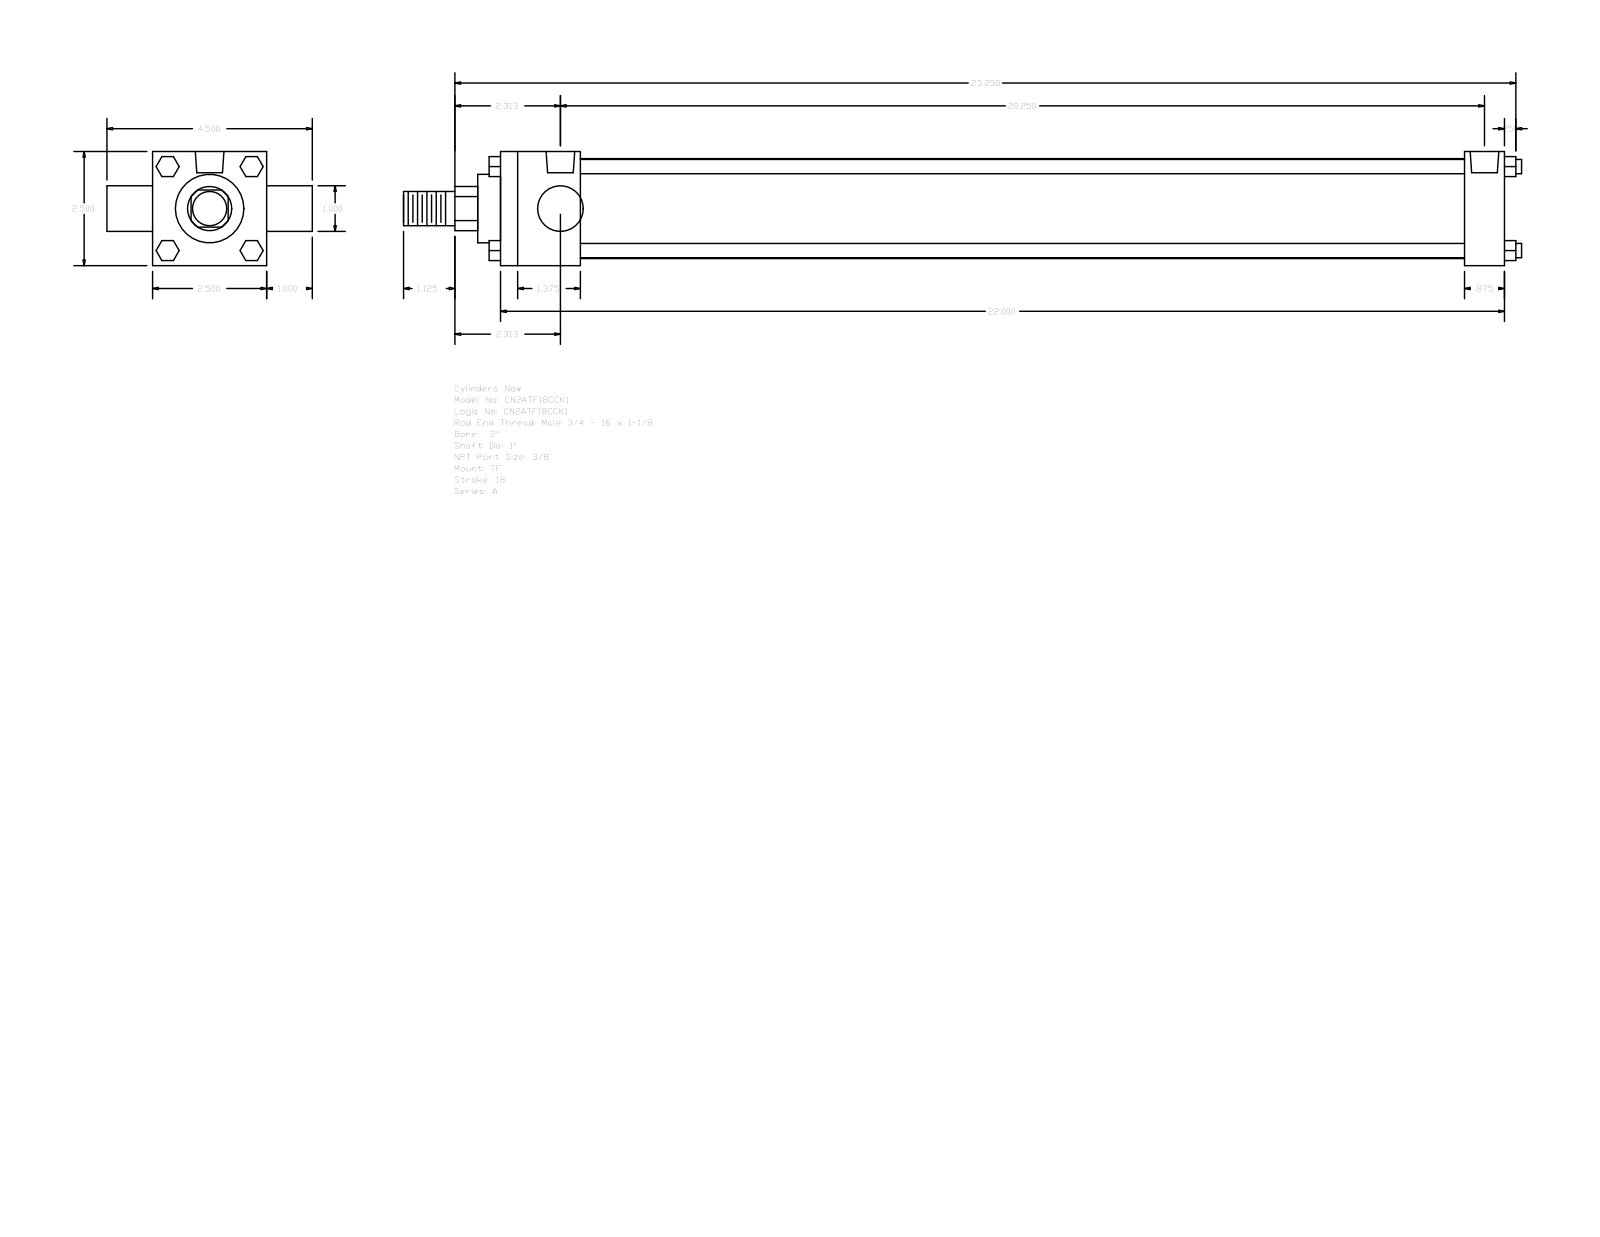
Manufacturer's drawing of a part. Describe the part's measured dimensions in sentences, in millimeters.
The part is named "A_TF__0200_1". Its 3-D file was written by "GSSL Pune (CONFIG_CONTROL_DESIGN)". It is 0 solids with 120 faces: 92 planar, 28 cylindrical and 0 other. Overall it measures 622.3 by 114.3 by 63.5 millimeters. Round holes: 3 of diameter 5.56, 2 of diameter 15.93. Round bosses or shafts: 4 of diameter 7.94, 2 of diameter 25.4, 1 of diameter 55.63, 1 of diameter 38.1, 1 of diameter 19.05. Partial cylindrical surfaces (rounded edges, fillets, slot ends): 1 of radius 12.29. The main face-to-face distances are 63.5, 558.8, 44.45, 536.58, 492.13, 514.35, 22.22, 25.4, 88.9, 571.5. The hole center spacings are 1.59, 3.98, 508.78, 510.37, 512.76, 514.35.
